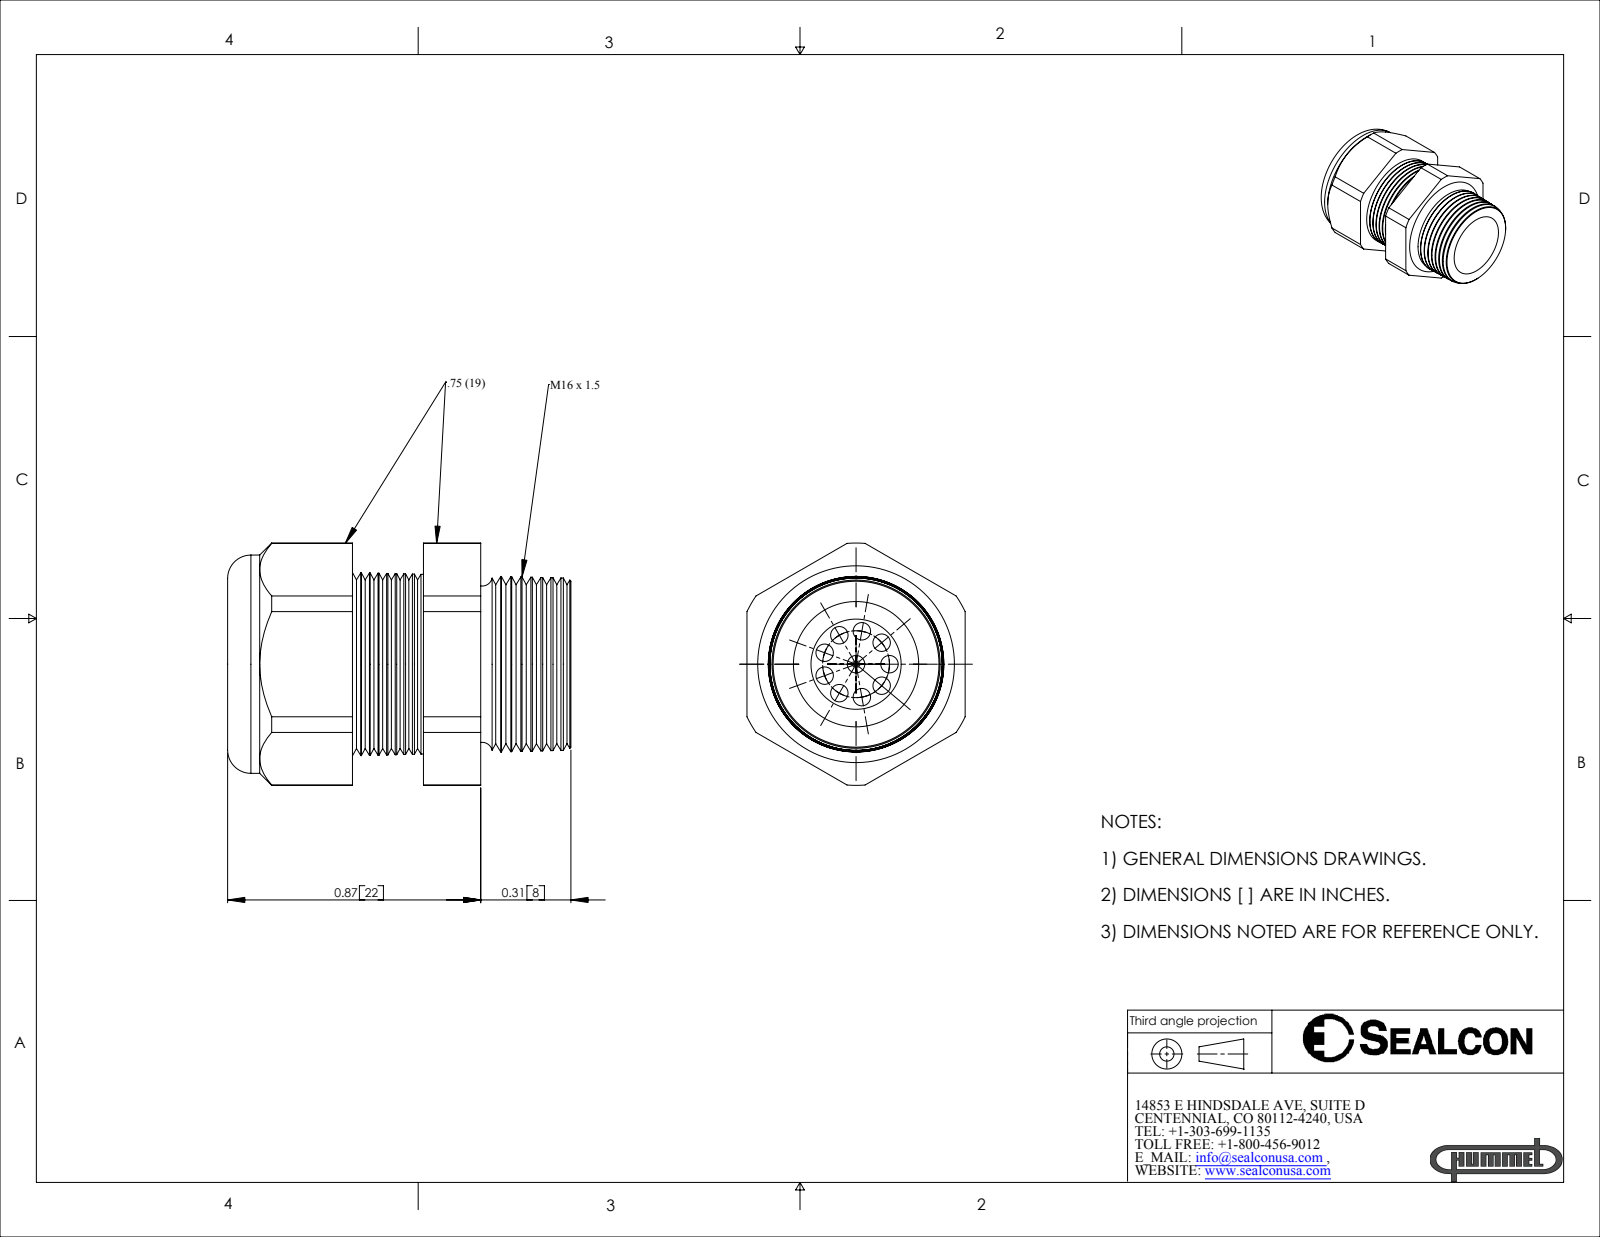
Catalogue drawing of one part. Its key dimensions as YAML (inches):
part_name: "CD16M5-GY"
step_written_by: "SolidWorks 2007 (CONFIG_CONTROL_DESIGN)"
units: inches
bodies: {solids: 2, faces: 170, planar: 20, cylindrical: 40, other: 110}
overall_size: [1.18, 0.833, 0.75]
volume: 0.334
surface_area: 6.298
round_holes:
  - {diameter: 0.06, count: 10}
  - {diameter: 0.29, count: 1}
  - {diameter: 0.31, count: 1}
round_bosses_or_shafts:
  - {diameter: 0.75, count: 1}
partial_cylinders:
  - {radius: 0.416, count: 1}
face_to_face_distances: [0.75, 0.673, 0.75, 0.429, 0.244, 0.87, 0.441, 0.197, 1.18, 0.751]
hole_center_spacings: [0.115, 0.199, 0.148, 0.226, 0.079, 0.078, 0.148, 0.115]
